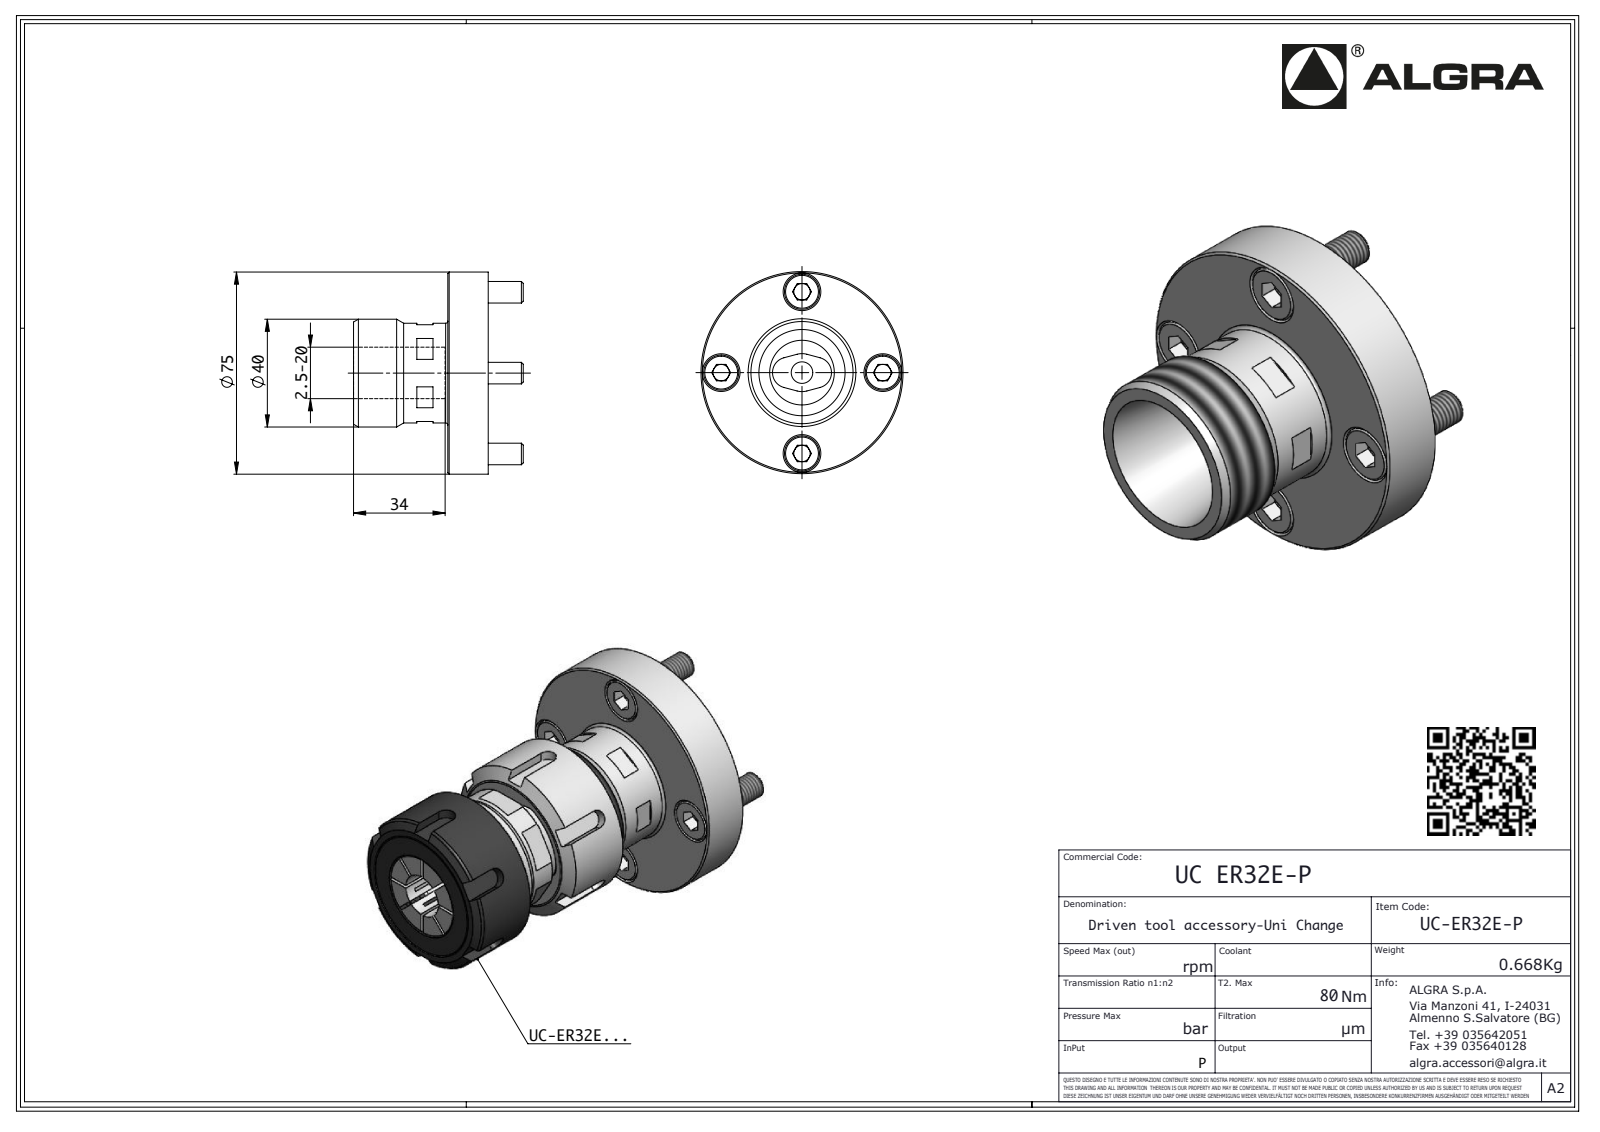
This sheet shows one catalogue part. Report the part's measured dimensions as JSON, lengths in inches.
{"part_name": "UCER32E-P", "step_written_by": "SolidWorks 2016 (AUTOMOTIVE_DESIGN)", "units": "inches", "bodies": {"solids": 1, "faces": 288, "planar": 195, "cylindrical": 33, "other": 60}, "overall_size": [2.953, 2.953, 2.48], "volume_in3": 6.674, "surface_area_in2": 27.86, "round_holes": [[0.083, 1]], "round_bosses_or_shafts": [[0.315, 4], [2.953, 1], [1.575, 1], [1.457, 1], [0.251, 1], [0.067, 1]], "partial_cylinders_radius": [[0.013, 7], [0.02, 7], [0.146, 7], [0.008, 1]], "face_to_face_distances": [0.591, 1.969, 1.378, 1.413, 0.512, 1.102, 2.48, 2.472, 1.961, 1.37]}
